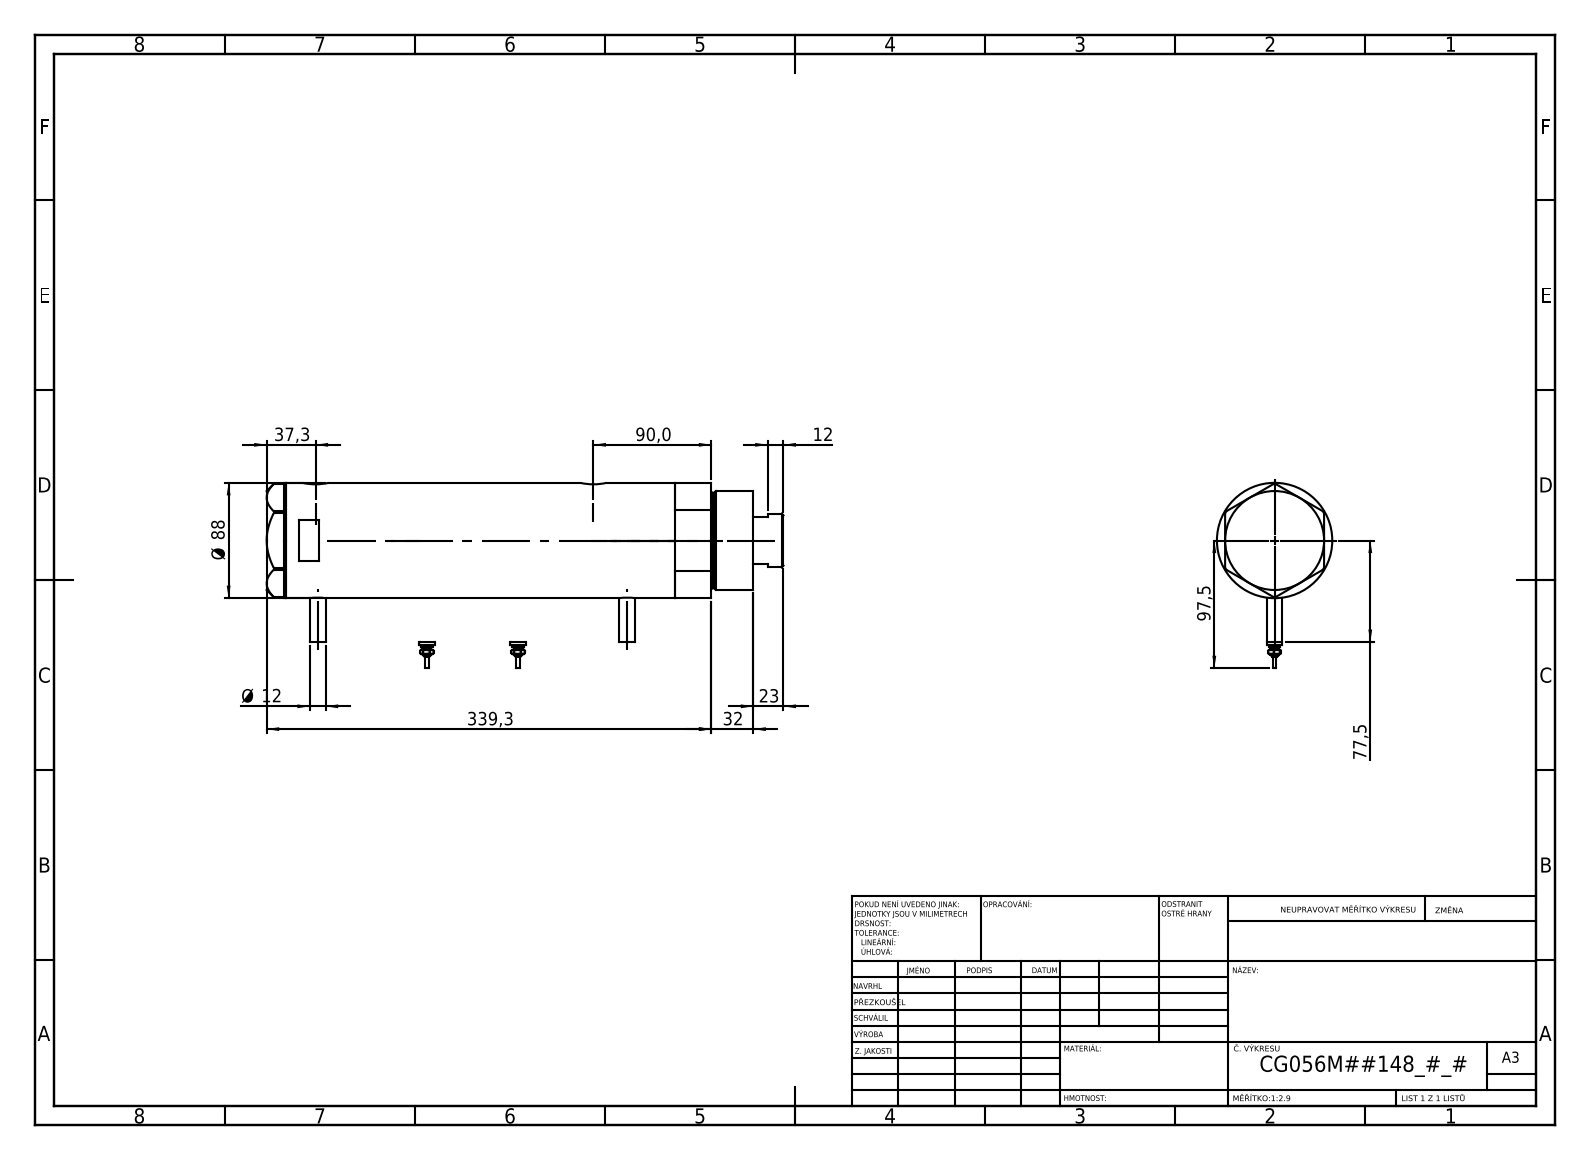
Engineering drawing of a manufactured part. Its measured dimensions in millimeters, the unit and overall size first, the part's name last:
Units: millimetres
Overall size (bounding box): 394.3 × 141.5 × 88
Round holes (diameter × count): ⌀12.5 ×2, ⌀13.16 ×2, ⌀20 ×2, ⌀14.5 ×1, ⌀42 ×1, ⌀43.5 ×1, ⌀56 ×1, ⌀60 ×1, ⌀80 ×1
Round bosses / shafts (diameter × count): ⌀12 ×4, ⌀9 ×2, ⌀7 ×2, ⌀4.5 ×2, ⌀2.5 ×2, ⌀88 ×1, ⌀75 ×1, ⌀73 ×1
Main face-to-face distances: 234.4, 26, 208.4, 15, 41, 249.4, 356.3, 371.3, 330.3, 121.9
Hole centre spacings: 1.7, 25.8, 210.3, 212, 236.1, 237.8
Volume: 2 044 000 mm³ · Surface area: 283 111 mm²
Bodies: 6 solids, 213 faces (80 planar, 69 cylindrical, 64 other)
Part name (STEP PRODUCT): V270CG_FRONT; V270CG_BACK; V270CG_VC; V270CG_MIDDLE (+1 more)
STEP written by: SolidWorks 2019 (CONFIG_CONTROL_DESIGN)
